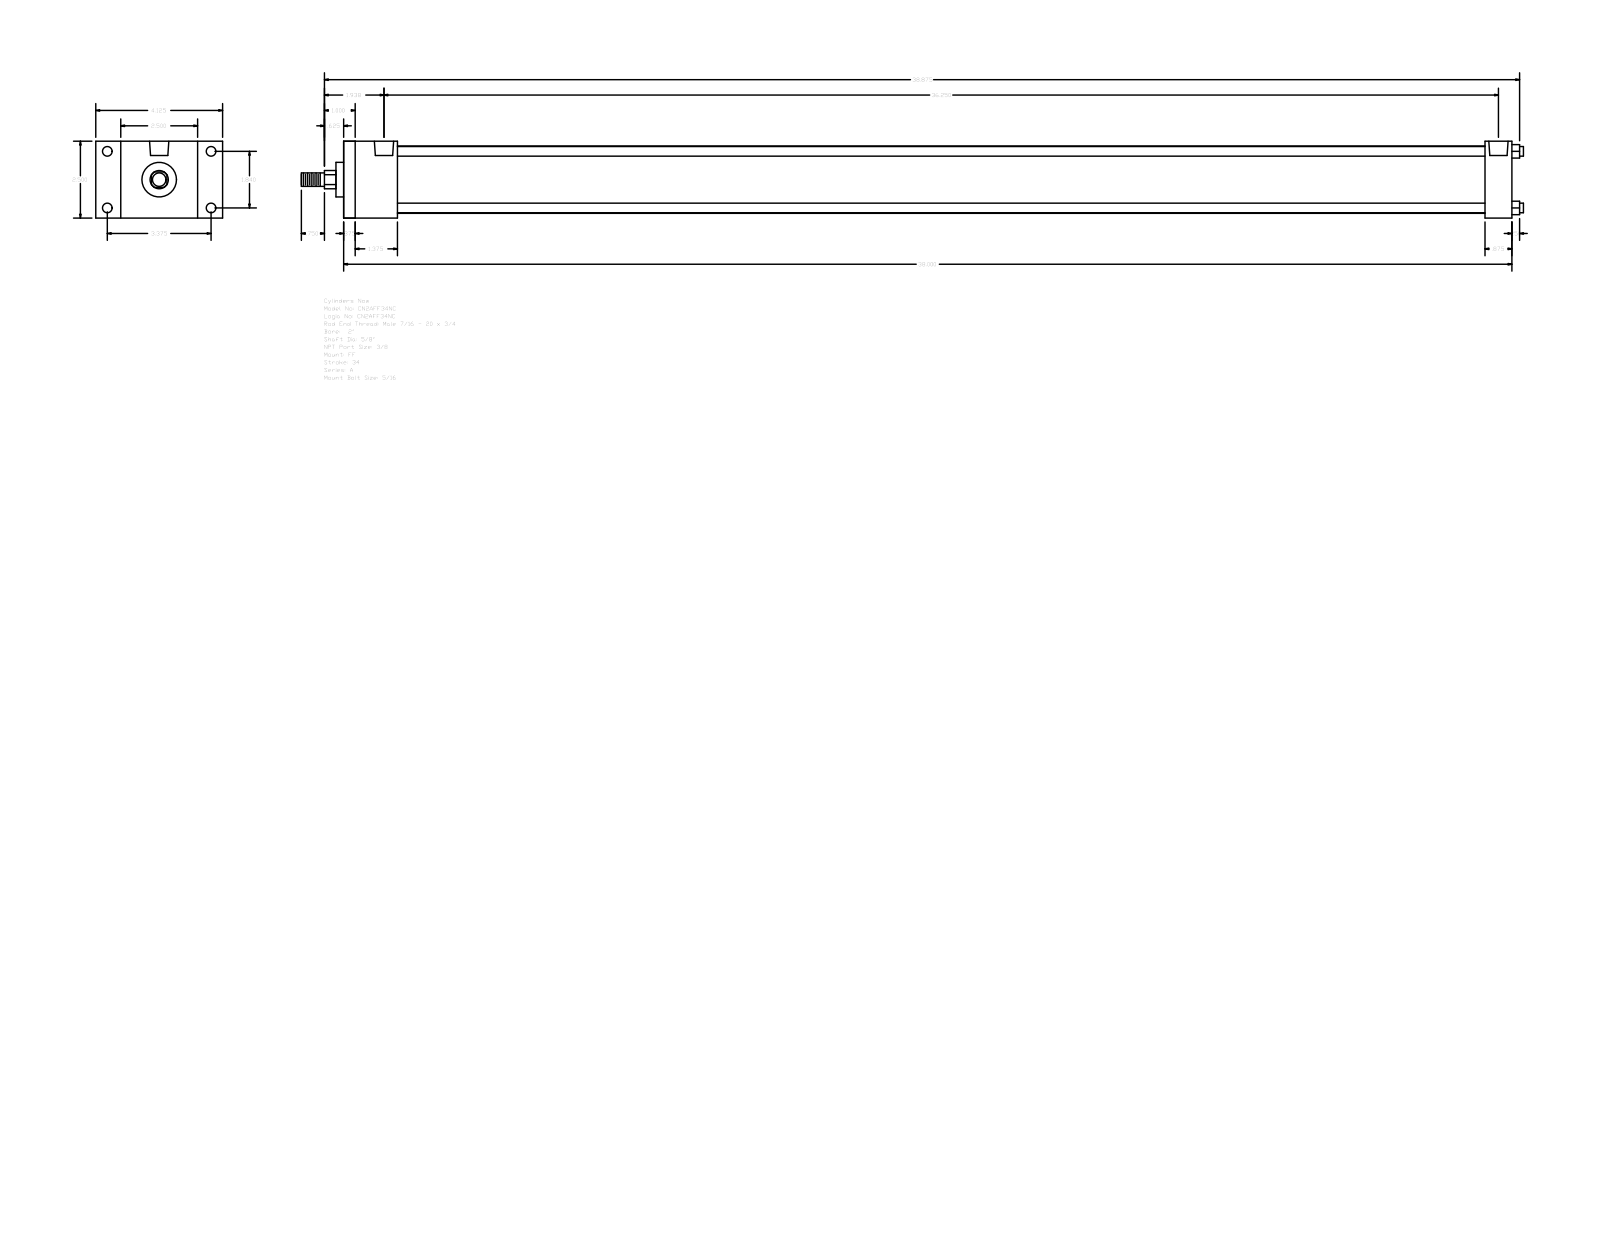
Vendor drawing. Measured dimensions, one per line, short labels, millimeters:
name: A_FF__0200_0.625
written by: GSSL Pune (CONFIG_CONTROL_DESIGN)
unit: mm
bodies: 0 solids, 92 faces (64 planar, 28 cylindrical, 0 other)
size: 1009.65 × 104.78 × 63.5
holes: 4× ⌀5.56, 4× ⌀7.94, 2× ⌀15.93
bosses: 4× ⌀7.94, 1× ⌀55.63, 1× ⌀28.57, 1× ⌀15.88, 1× ⌀11.11
rounds: 1× R7.54
face distances: 63.5, 965.2, 9.52, 955.68, 34.93, 44.45, 942.97, 933.45, 898.52, 920.75
hole spacings: 46.74, 85.72, 97.63, 912.8, 3.97, 3.98, 916.77, 916.78
